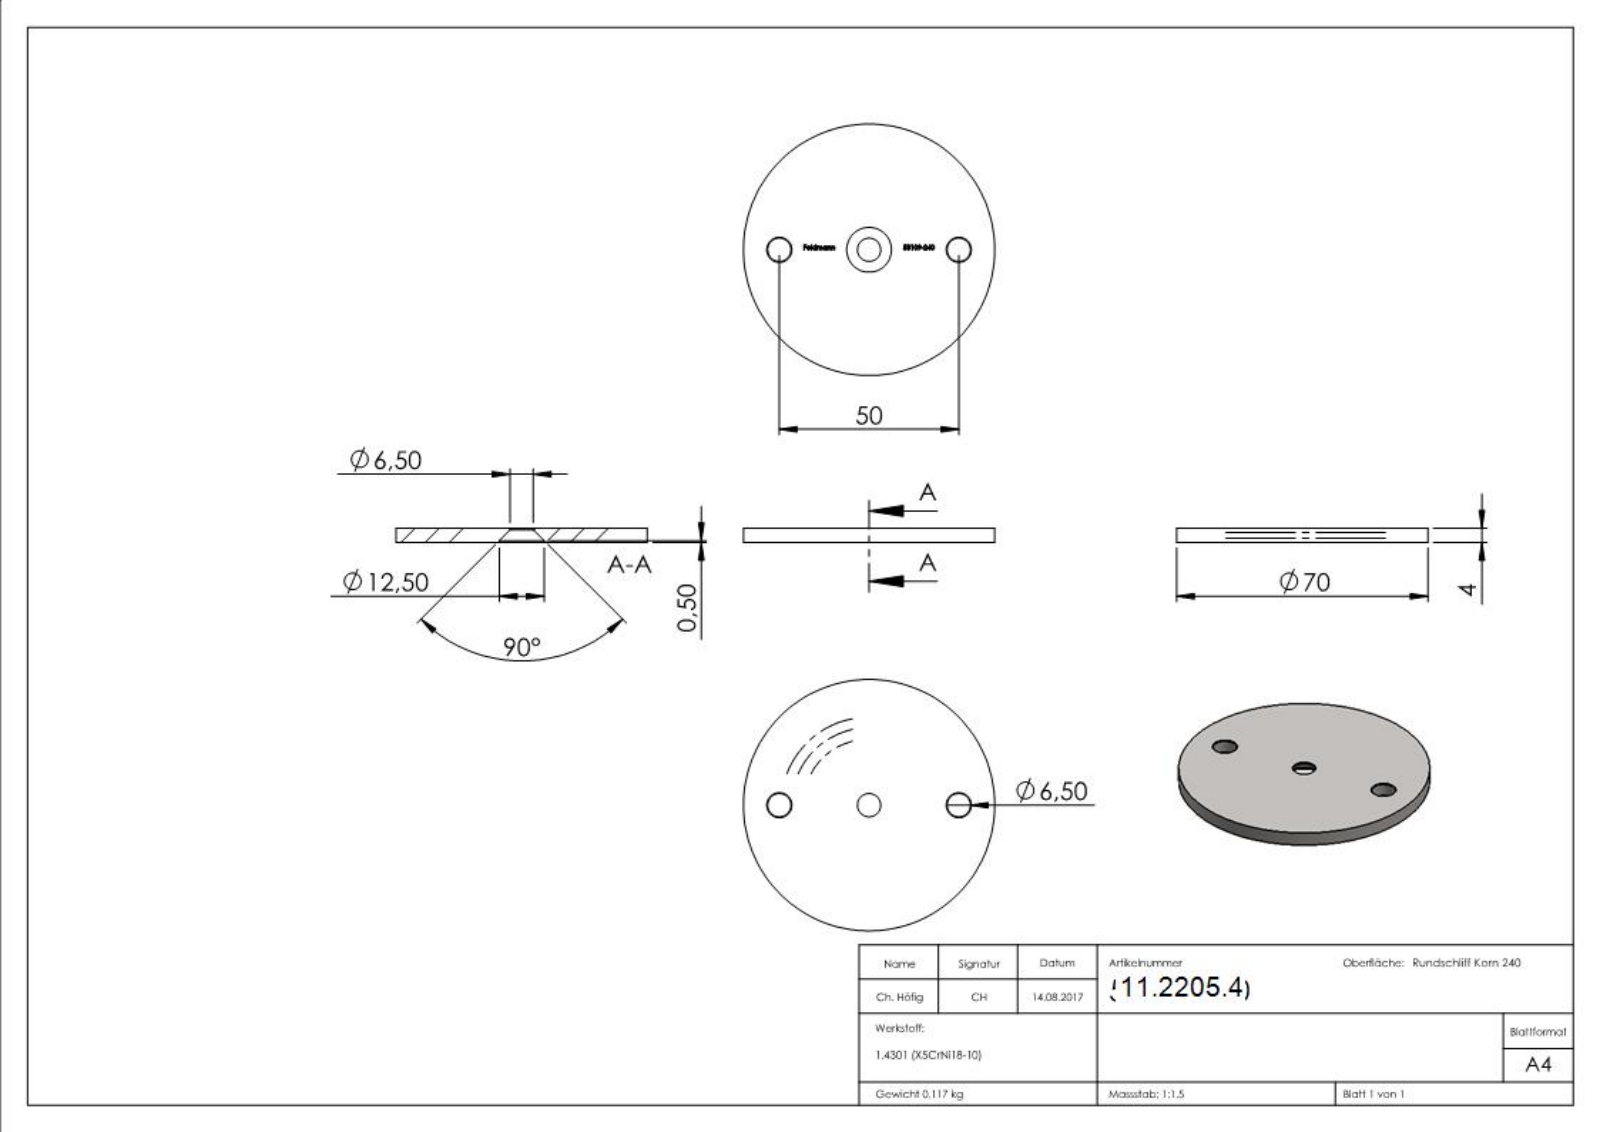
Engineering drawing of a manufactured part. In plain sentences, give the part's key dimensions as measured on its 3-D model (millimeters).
The part is named "53109-240". Its 3-D file was written by "SolidWorks 2015 (CONFIG_CONTROL_DESIGN)". It is 1 solid with 244 faces: 121 planar, 10 cylindrical and 113 other. Overall it measures 70 by 70 by 4 millimeters. Its volume is 14 827 cubic millimeters and its surface area 8 606 square millimeters. Round holes: 3 of diameter 6.5, 1 of diameter 12.5. Round bosses or shafts: 1 of diameter 70. The main face-to-face distances are 4, 3.9, 0.39, 2.97, 28.13, 2.02, 30.15, 33.03, 4.9, 0.44. The hole center spacings are 25, 50.
